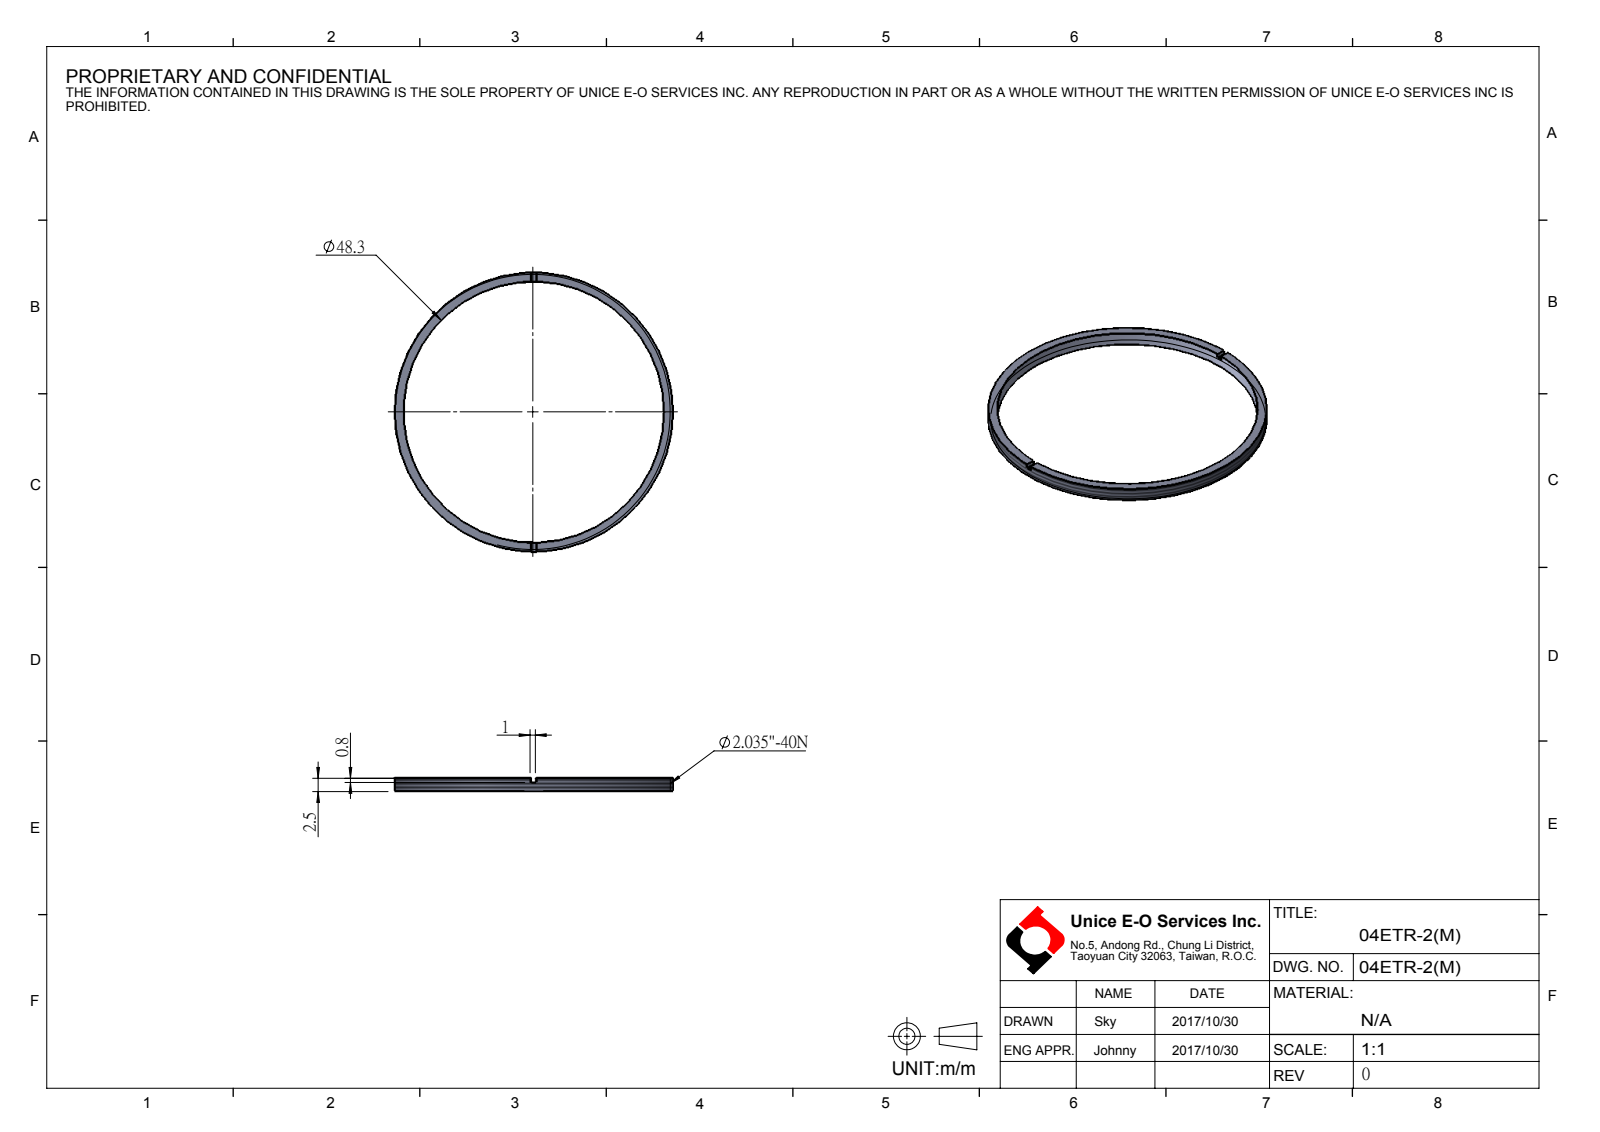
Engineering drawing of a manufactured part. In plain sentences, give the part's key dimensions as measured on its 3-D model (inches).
The part is named "04ETR-2(M)". Its 3-D file was written by "SolidWorks 2016 (AUTOMOTIVE_DESIGN)". It is 1 solid with 13 faces: 9 planar, 4 cylindrical and 0 other. Overall it measures 2.035 by 2.035 by 0.098 inches. Its volume is 0.04 cubic inches and its surface area 2.046 square inches. Round holes: 1 of diameter 1.902. Round bosses or shafts: 1 of diameter 2.035. The main face-to-face distances are 0.098, 0.067, 0.031, 0.039.
